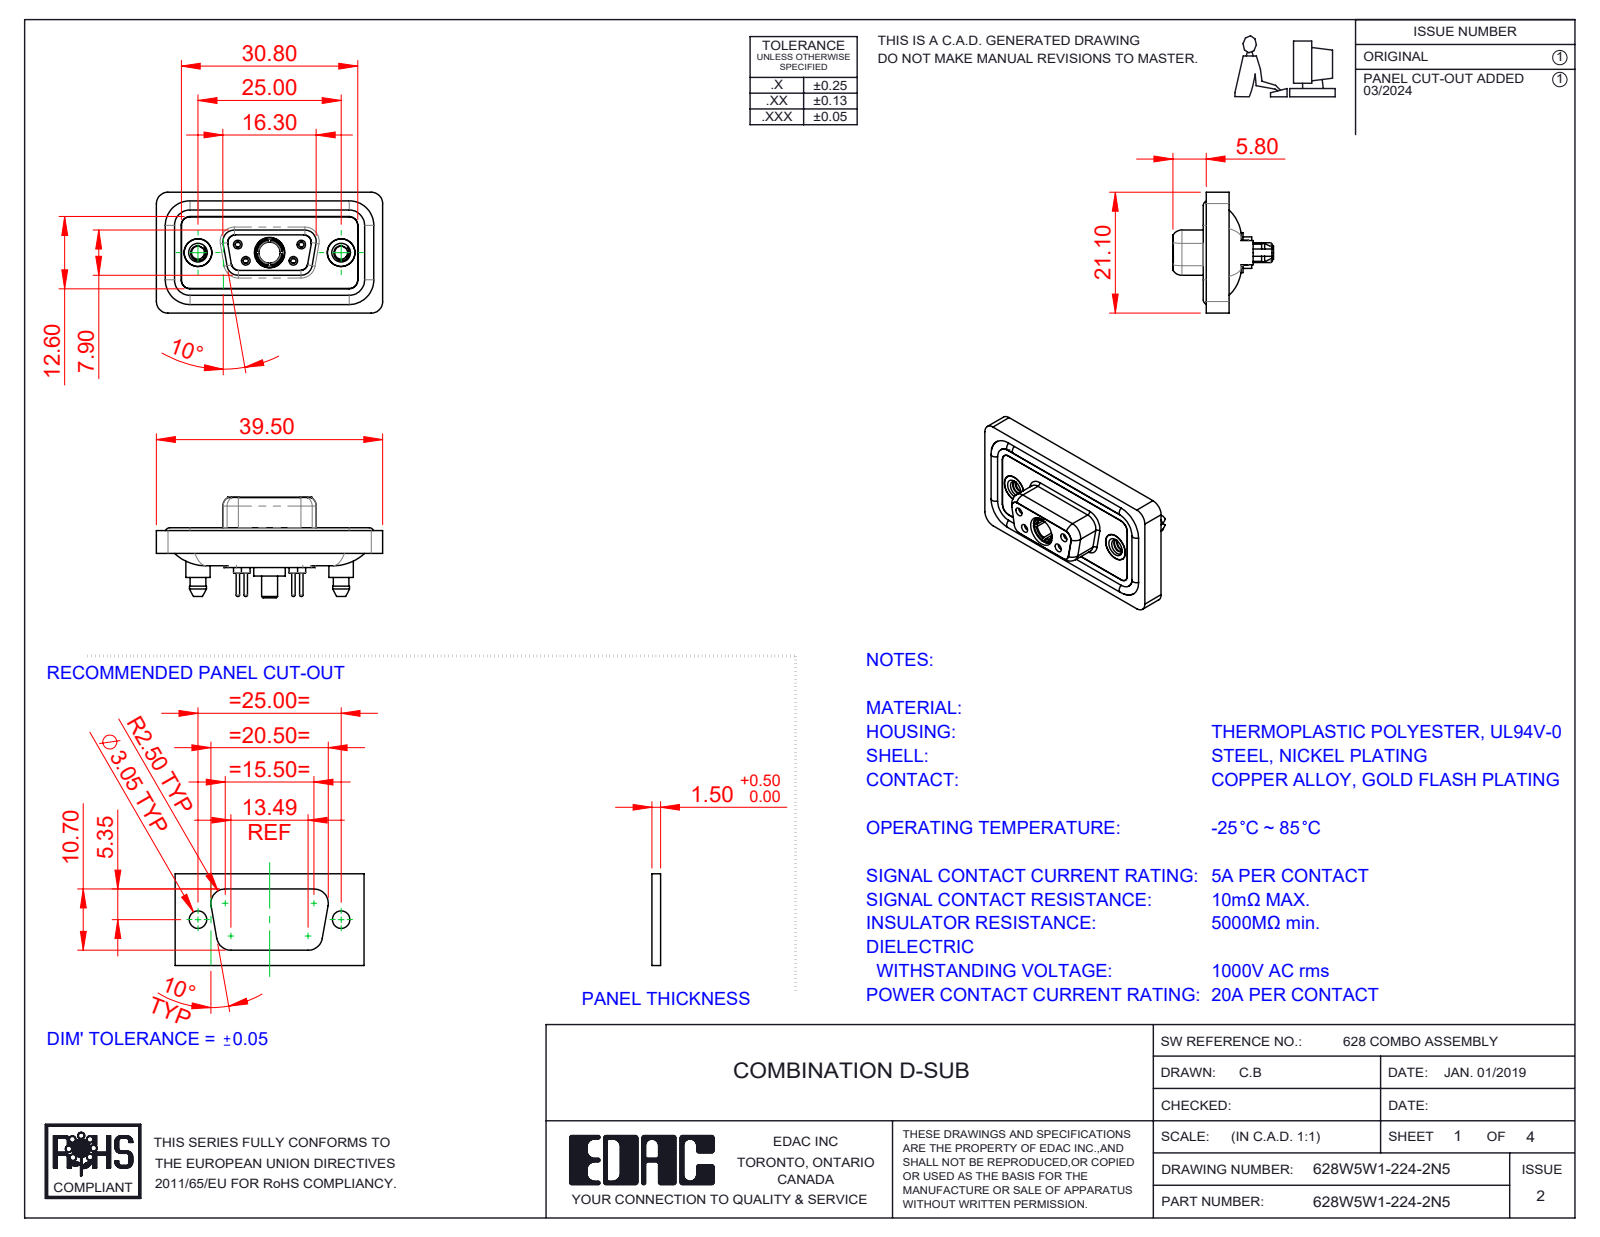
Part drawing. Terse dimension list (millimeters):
name: Power Socket_20A S; 628W5W1-224-2N5; 628Combo Shell Rear_09 Contacts; 628Combo Waterproof Housing_09 Contacts (+5 more)
written by: SolidWorks 2023 (CONFIG_CONTROL_DESIGN)
unit: mm
bodies: 13 solids, 730 faces (210 planar, 319 cylindrical, 201 other)
size: 39.5 × 21.1 × 17.55
volume: 4 901 mm³; area: 7 968 mm²
holes: 4× ⌀0.9, 4× ⌀1.1, 4× ⌀1.5, 4× ⌀2, 3× ⌀4.85, 2× ⌀1.6, 2× ⌀1.7, 2× ⌀2.26, 2× ⌀4, 2× ⌀4.05, 2× ⌀5, 1× ⌀3.7
bosses: 6× ⌀1.6, 4× ⌀2.2, 4× ⌀0.6, 2× ⌀5.4, 2× ⌀4.95, 2× ⌀4.8, 2× ⌀4.25, 1× ⌀5.5
rounds: 24× R1.5, 18× R2, 10× R1.6, 8× R1.35, 4× R0.25, 4× R0.5, 4× R0.6, 4× R0.65
face distances: 0.4, 2.9, 1.1, 1.8, 1.6, 0.5, 5.65, 7.45, 5.35, 3.6
hole spacings: 3.16, 5.72, 7.1, 12.5, 18.1, 4.39, 4.4, 8.31
